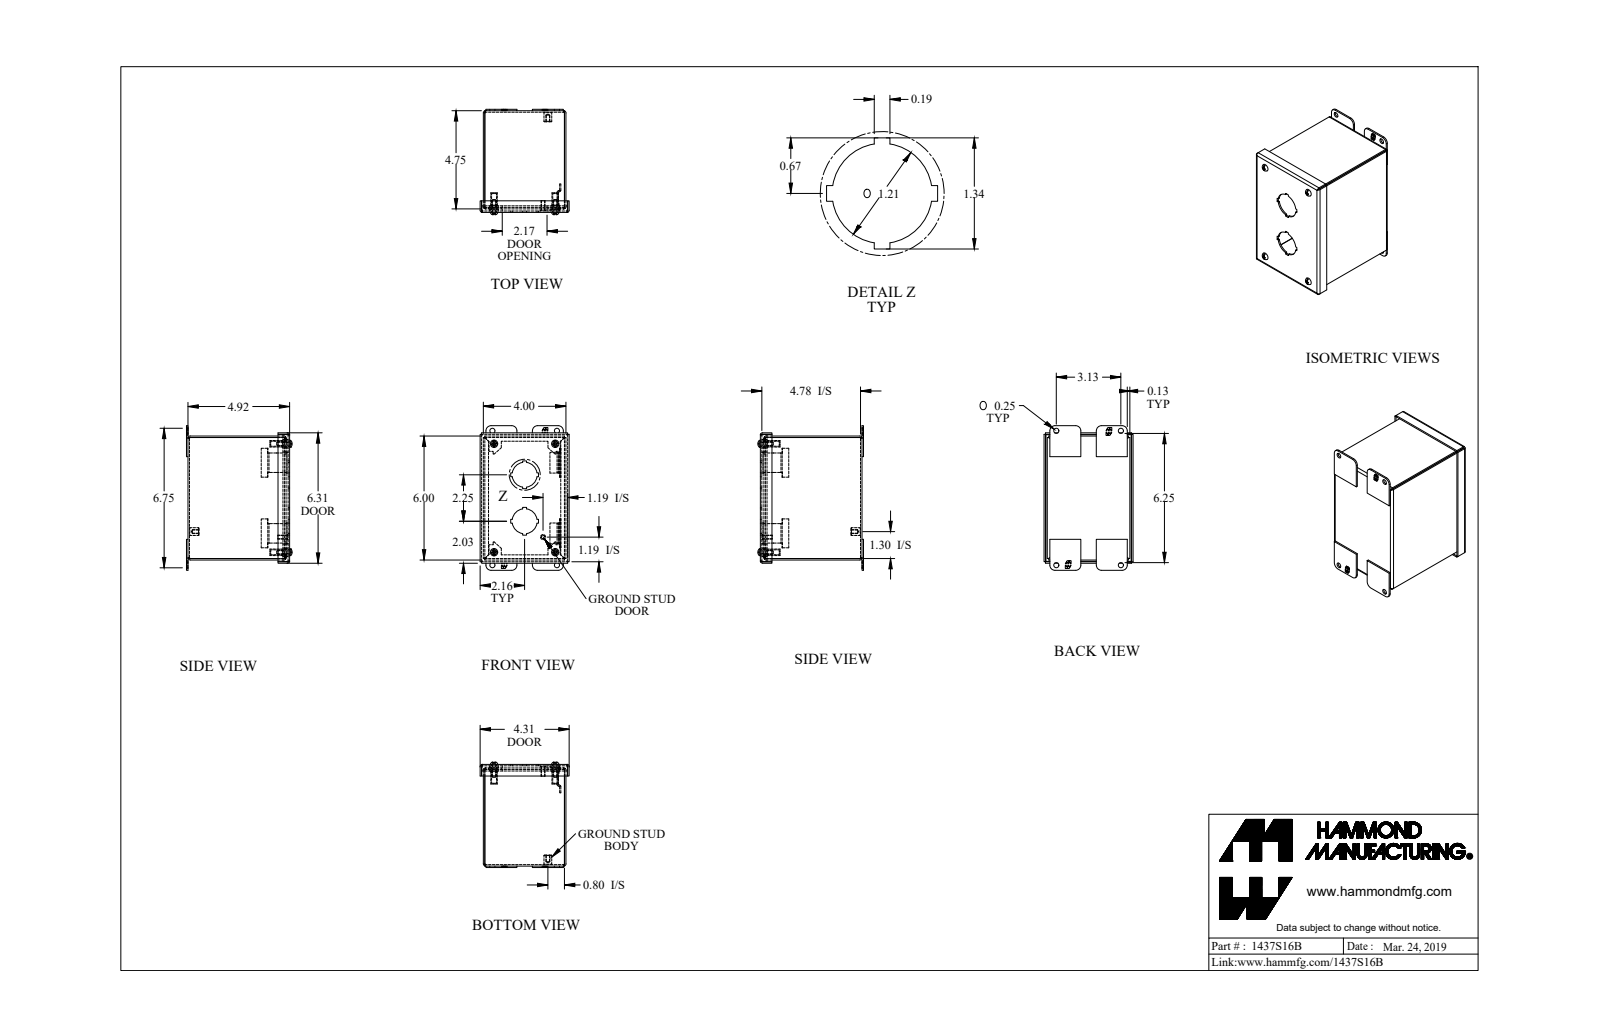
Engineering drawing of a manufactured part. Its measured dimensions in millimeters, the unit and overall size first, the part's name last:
Units: millimetres
Overall size (bounding box): 177.8 × 129.6 × 109.5
Round holes (diameter × count): ⌀6.4 ×8, ⌀1.7 ×4, ⌀6.1 ×4, ⌀6.4 ×4, ⌀10.3 ×4, ⌀30.7 ×2, ⌀4 ×1
Round bosses / shafts (diameter × count): ⌀4.8 ×5, ⌀10.3 ×4, ⌀8 ×4, ⌀3.8 ×4, ⌀9.5 ×1, ⌀6.4 ×1
Partial cylindrical surfaces — rounded edges, fillets, slot ends (radius × count): R0.9 ×12, R2.7 ×12, R6.4 ×8, R0.7 ×4, R2.2 ×4, R3.2 ×4, R4.3 ×4
Main face-to-face distances: 1.8, 99.8, 123.2, 150.6, 125, 101.6, 97.9, 121.4, 4, 152.4
Hole centre spacings: 16, 75.2, 78.9, 102.4, 133.4, 149.2, 75.2, 53.5
Volume: 229 100 mm³ · Surface area: 242 600 mm²
Bodies: 23 solids, 637 faces (447 planar, 160 cylindrical, 30 other)
Part name (STEP PRODUCT): 1437S16B_Default
STEP written by: SolidWorks 2019 (CONFIG_CONTROL_DESIGN)
